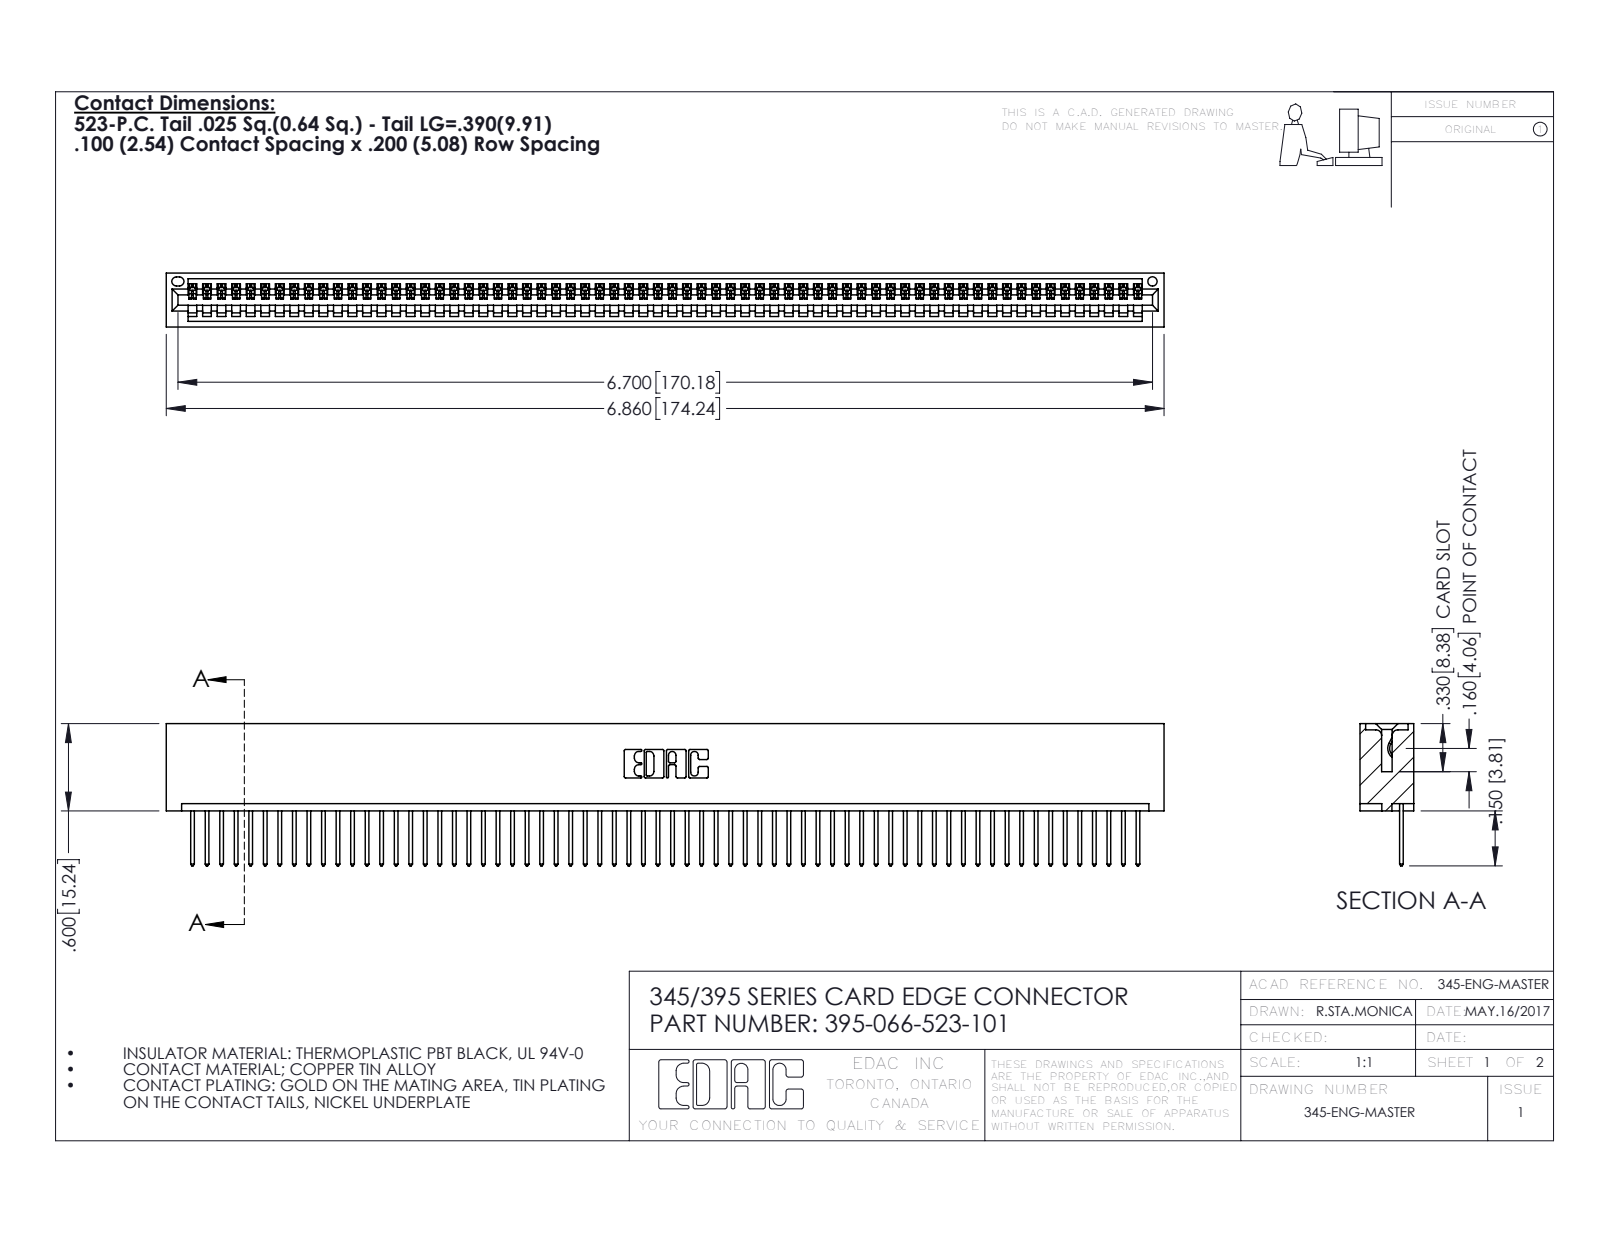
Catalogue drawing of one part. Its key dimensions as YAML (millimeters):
part_name: "345-292-001_345-293-123; 395-066-523-101; 345 Part_No Mounting Lugs"
step_written_by: "SolidWorks 2016 (CONFIG_CONTROL_DESIGN)"
units: millimeters
bodies: {solids: 67, faces: 3946, planar: 2716, cylindrical: 1230, other: 0}
overall_size: [174.2, 24.8, 9.4]
volume: 17300
surface_area: 23590
round_holes:
  - {diameter: 1.6, count: 1}
partial_cylinders:
  - {radius: 0.2, count: 132}
  - {radius: 0.3, count: 132}
  - {radius: 0.3, count: 22}
  - {radius: 0.2, count: 6}
  - {radius: 0.8, count: 6}
  - {radius: 0.7, count: 3}
  - {radius: 0.8, count: 2}
  - {radius: 1, count: 2}
face_to_face_distances: [7.6, 1.8, 9.4, 2.5, 6.9, 0.6, 5.1, 5.7, 3.8, 1.8]
